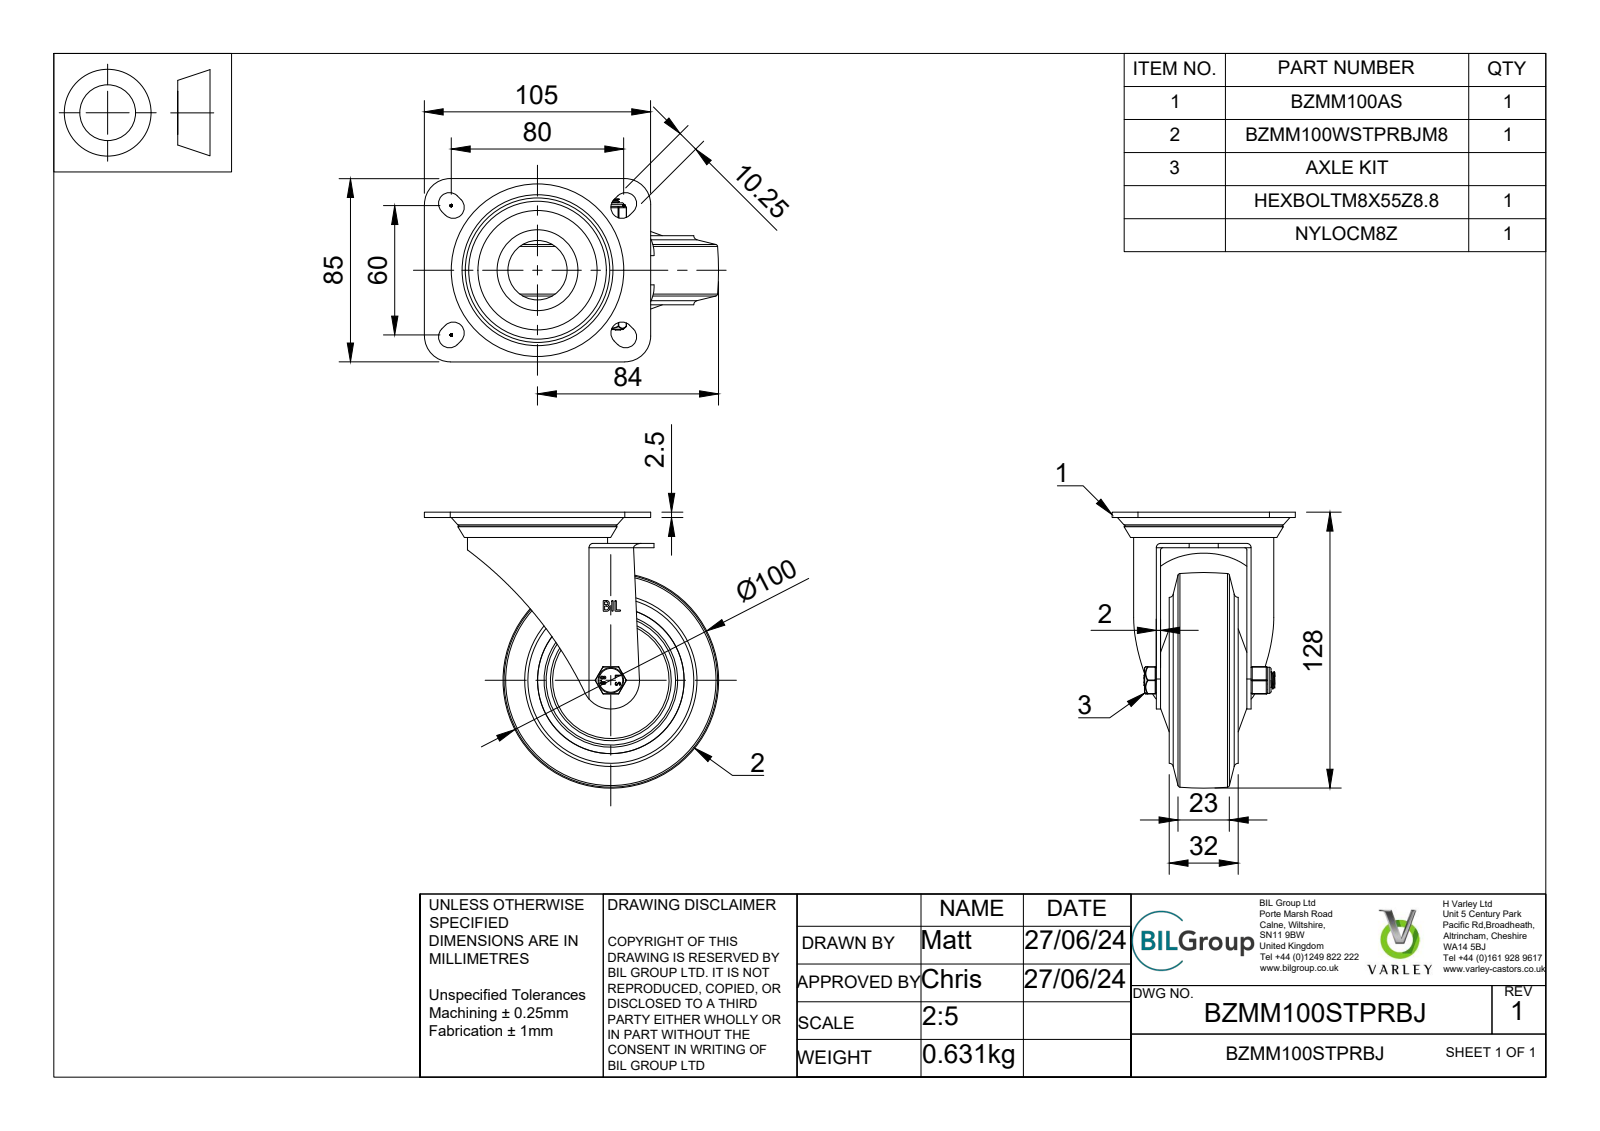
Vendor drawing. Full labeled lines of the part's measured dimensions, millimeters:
Part name (STEP PRODUCT): BZMM100STPRBJ v3; BZMM100WSTPRBJM8 v1; 65 SHORE A THERMOPLASTIC RUBBER TYRE; POLYPROPYLENE RIM (+8 more)
STEP written by: Autodesk Translation Framework v13.14.0.145 (AUTOMOTIVE_DESIGN)
Units: millimetres
Bodies: 47 solids, 756 faces (269 planar, 189 cylindrical, 298 other)
Overall size (bounding box): 136.5 × 128 × 85
Volume: 234 730 mm³ · Surface area: 128 051 mm²
Round holes (diameter × count): ⌀0.66 ×2, ⌀8 ×1, ⌀8.2 ×1, ⌀8.25 ×1, ⌀8.6 ×1, ⌀11.5 ×1, ⌀15 ×1, ⌀20 ×1, ⌀22.5 ×1, ⌀27.5 ×1, ⌀30 ×1, ⌀31 ×1
Round bosses / shafts (diameter × count): ⌀65 ×1, ⌀56 ×1, ⌀44 ×1, ⌀35 ×1, ⌀31.5 ×1, ⌀30.5 ×1, ⌀23 ×1, ⌀18 ×1
Partial cylindrical surfaces — rounded edges, fillets, slot ends (radius × count): R0.5 ×18, R0.25 ×12, R5.12 ×8, R12 ×5, R0.33 ×4, R0.64 ×4, R1 ×4, R0.63 ×2
Main face-to-face distances: 2, 2.5, 13.5, 4, 6, 36, 38, 42, 24.5, 14.5
Hole centre spacings: 3.22, 2.49
